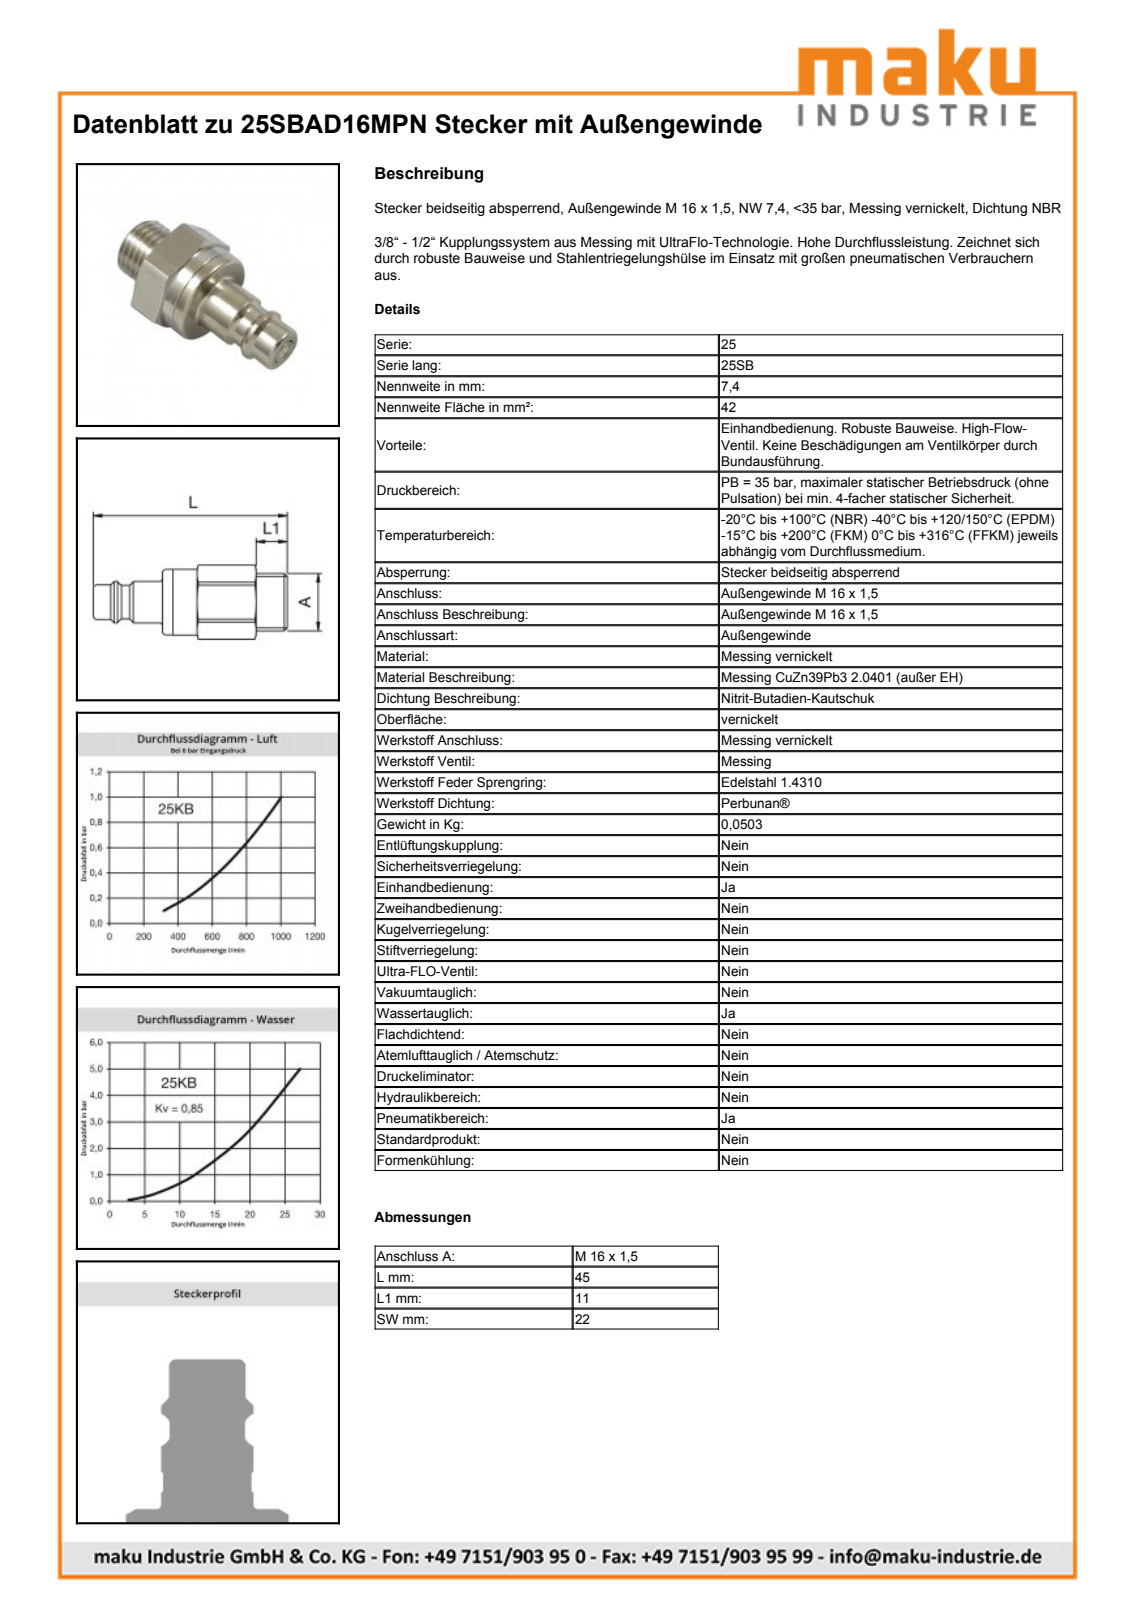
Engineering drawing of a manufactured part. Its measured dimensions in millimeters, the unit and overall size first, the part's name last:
Units: millimetres
Overall size (bounding box): 45.1 × 24.44 × 23.93
Round holes (diameter × count): ⌀8.6 ×1, ⌀17.15 ×1
Round bosses / shafts (diameter × count): ⌀21 ×1, ⌀16.5 ×1, ⌀16 ×1, ⌀12 ×1, ⌀10 ×1, ⌀9.75 ×1
Partial cylindrical surfaces — rounded edges, fillets, slot ends (radius × count): R12.4 ×1
Main face-to-face distances: 22, 11.1, 14, 25.1, 20, 34, 45.1, 23, 3, 11
Volume: 9 504 mm³ · Surface area: 3 240 mm²
Bodies: 1 solid, 54 faces (16 planar, 15 cylindrical, 23 other)
Part name (STEP PRODUCT): D110758
STEP written by: Autodesk Inventor 2013 (AUTOMOTIVE_DESIGN)
